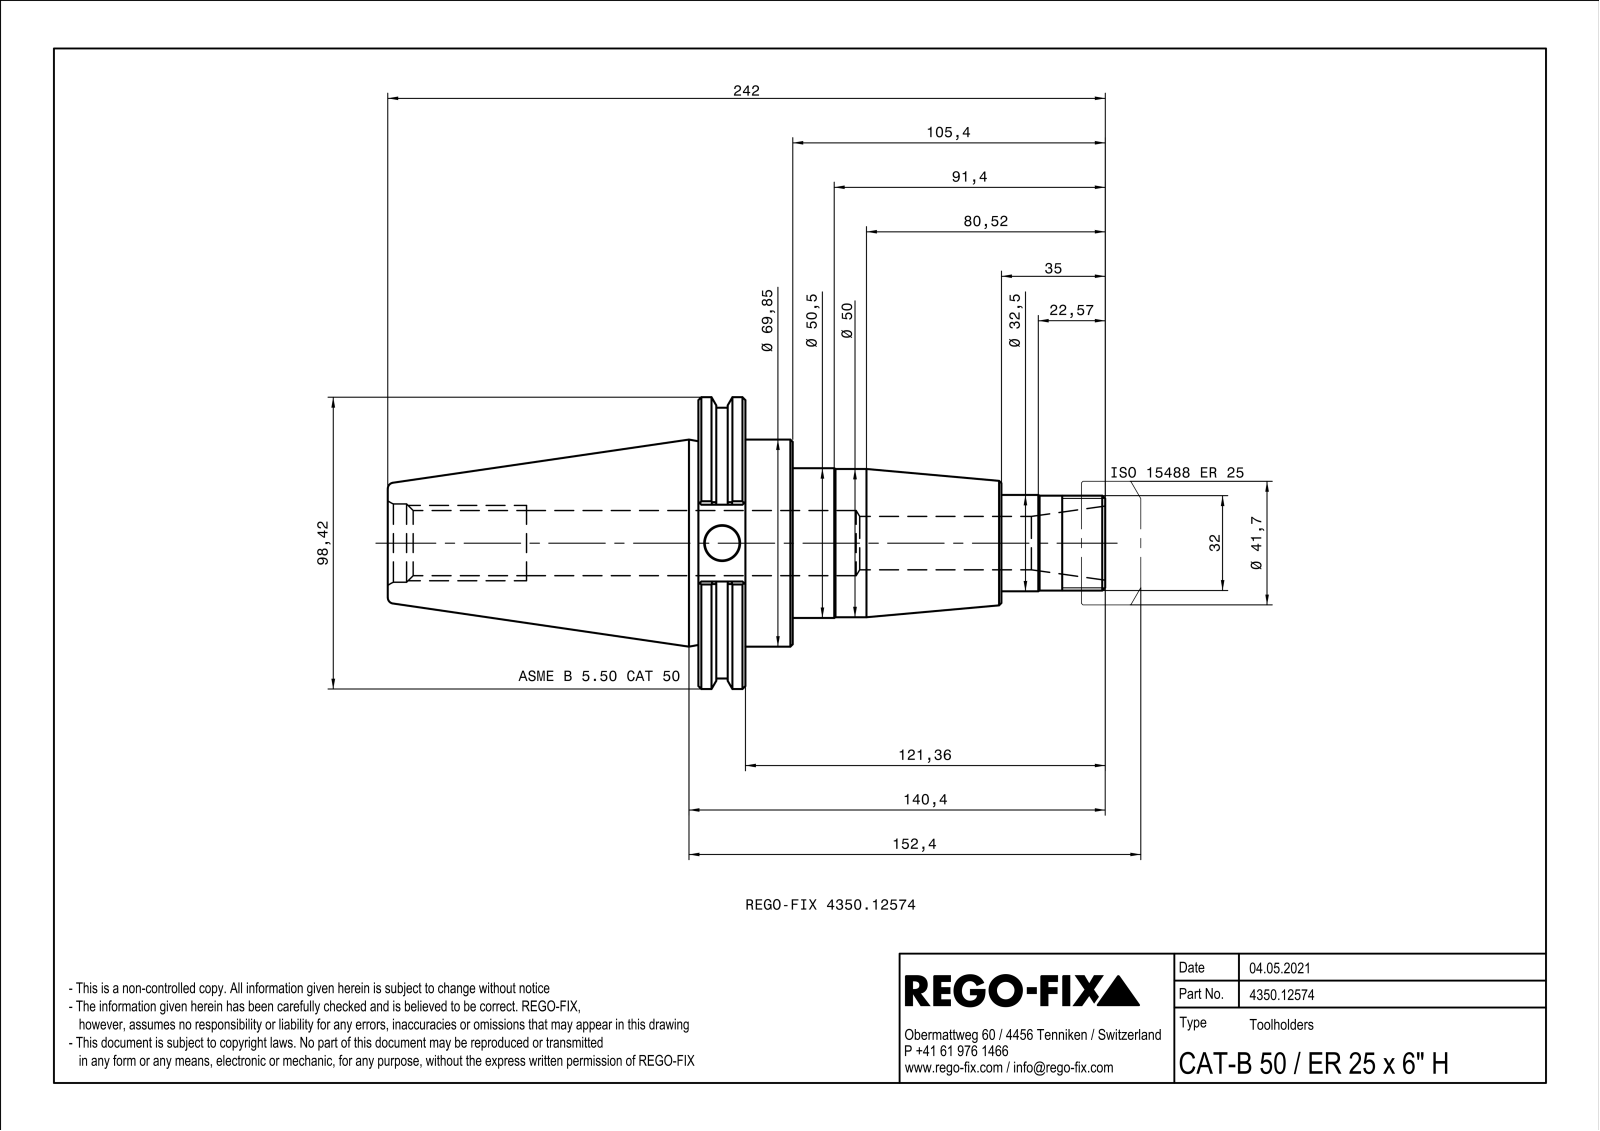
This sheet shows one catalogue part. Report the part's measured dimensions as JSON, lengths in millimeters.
{"part_name": "NOCUT", "step_written_by": "SIEMENS PLM Software Solid Edge ST10 (AUTOMOTIVE_DESIGN)", "units": "millimeters", "bodies": {"solids": 1, "faces": 134, "planar": 36, "cylindrical": 45, "other": 53}, "overall_size": [242, 98.42, 94.39], "volume_mm3": 496795, "surface_area_mm2": 68765, "round_holes": [[3.24, 2], [3.9, 2], [10.11, 1], [11.7, 1], [18, 1], [21.96, 1], [21.96, 1], [26.4, 1]], "round_bosses_or_shafts": [[98.42, 1], [91.3, 1], [69.85, 1], [50.5, 1], [50, 1], [32.5, 1], [32, 1]], "partial_cylinders_radius": [[0.5, 12]], "face_to_face_distances": [15.87, 15.96, 31.83, 136.6, 120.64, 104.77, 70.4, 86.36, 102.23, 207]}
